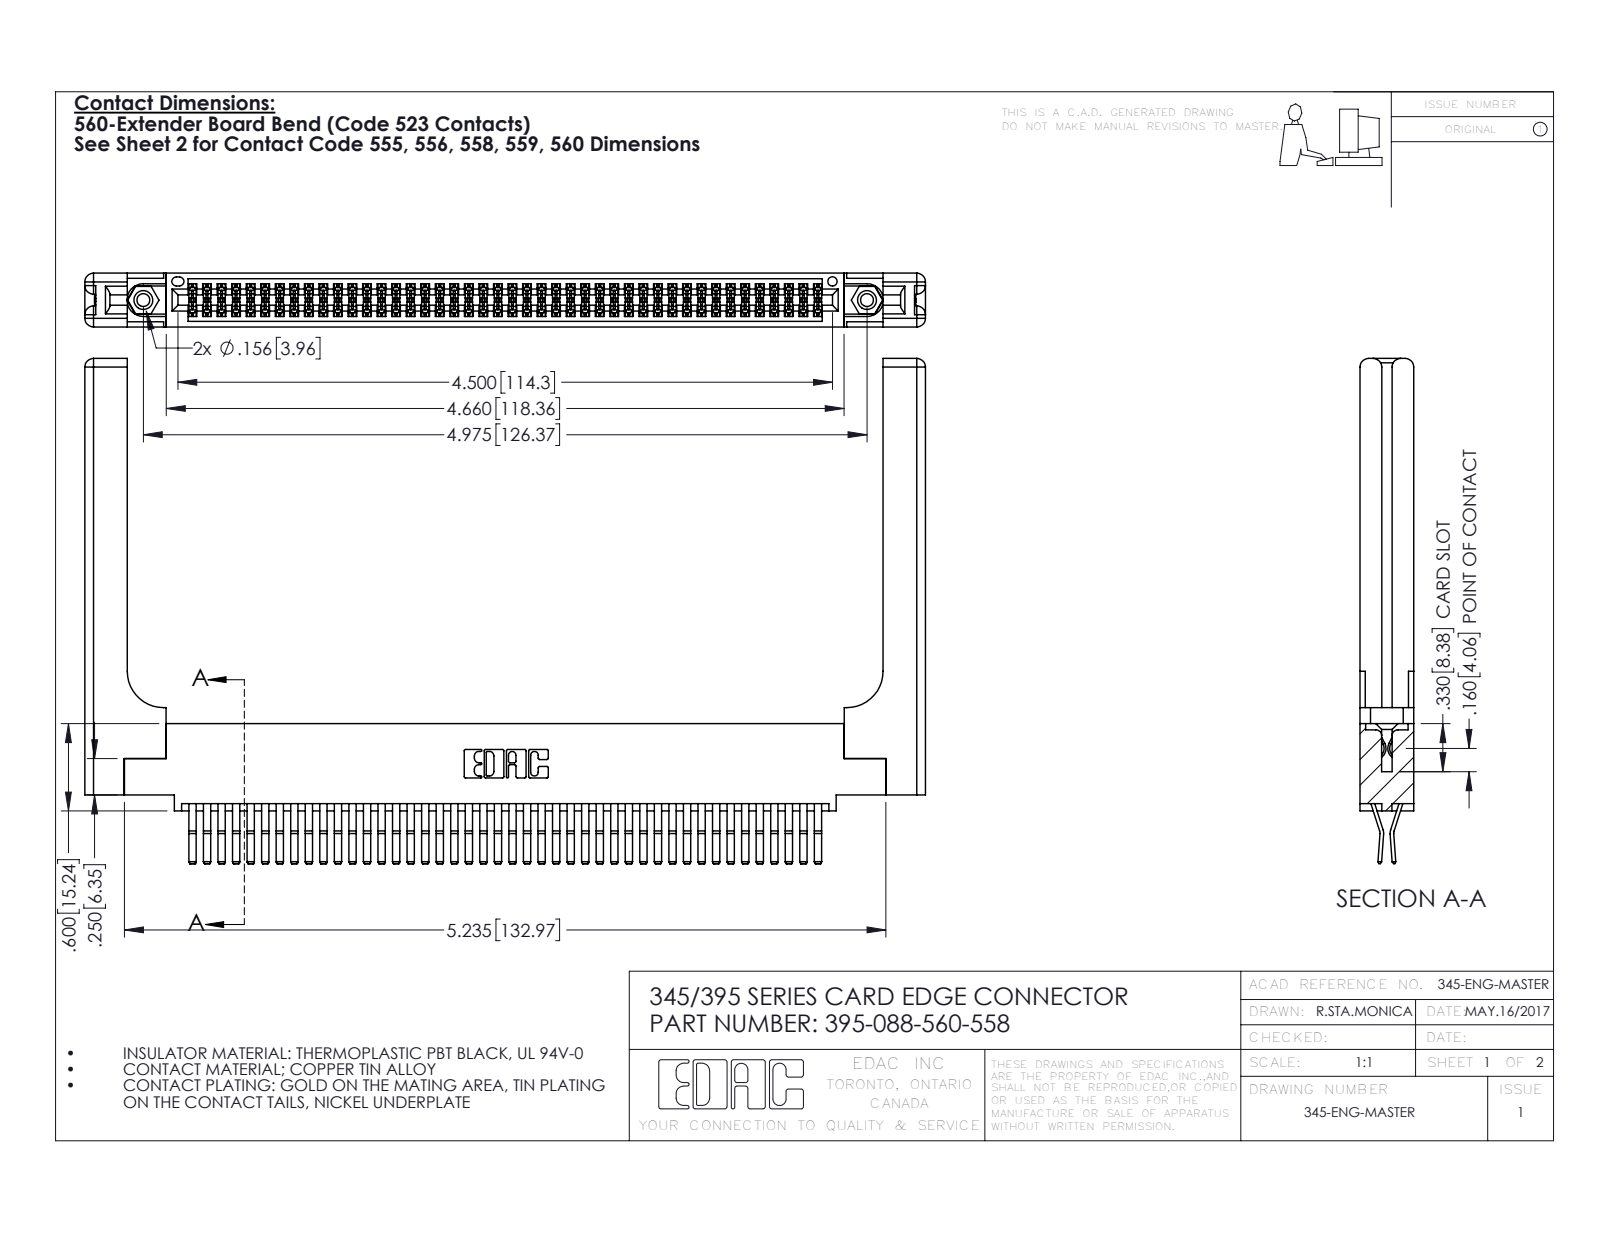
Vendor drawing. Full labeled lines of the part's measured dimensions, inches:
Part name (STEP PRODUCT): 345-292-001_560 Tail; 345-220-058_345-220-058; 395-088-560-558; 345-250-001_345-250-001-102 (+1 more)
STEP written by: SolidWorks 2016 (CONFIG_CONTROL_DESIGN)
Units: inches
Bodies: 93 solids, 4962 faces (3136 planar, 1766 cylindrical, 60 other)
Overall size (bounding box): 5.779 × 3.472 × 0.37
Volume: 1.419 in³ · Surface area: 44.21 in²
Round holes (diameter × count): ⌀0.089 ×2, ⌀0.125 ×2, ⌀0.156 ×2, ⌀0.064 ×1
Round bosses / shafts (diameter × count): ⌀0.155 ×2
Partial cylindrical surfaces — rounded edges, fillets, slot ends (radius × count): R0.006 ×132, R0.01 ×22, R0.06 ×16, R0.007 ×6, R0.031 ×6, R0.026 ×3, R0.01 ×2, R0.014 ×2
Main face-to-face distances: 0.072, 0.37, 0.298, 0.025, 0.2, 0.098, 0.272, 0.225, 0.148, 0.15
Hole centre spacings: 0.27, 4.739, 4.975
